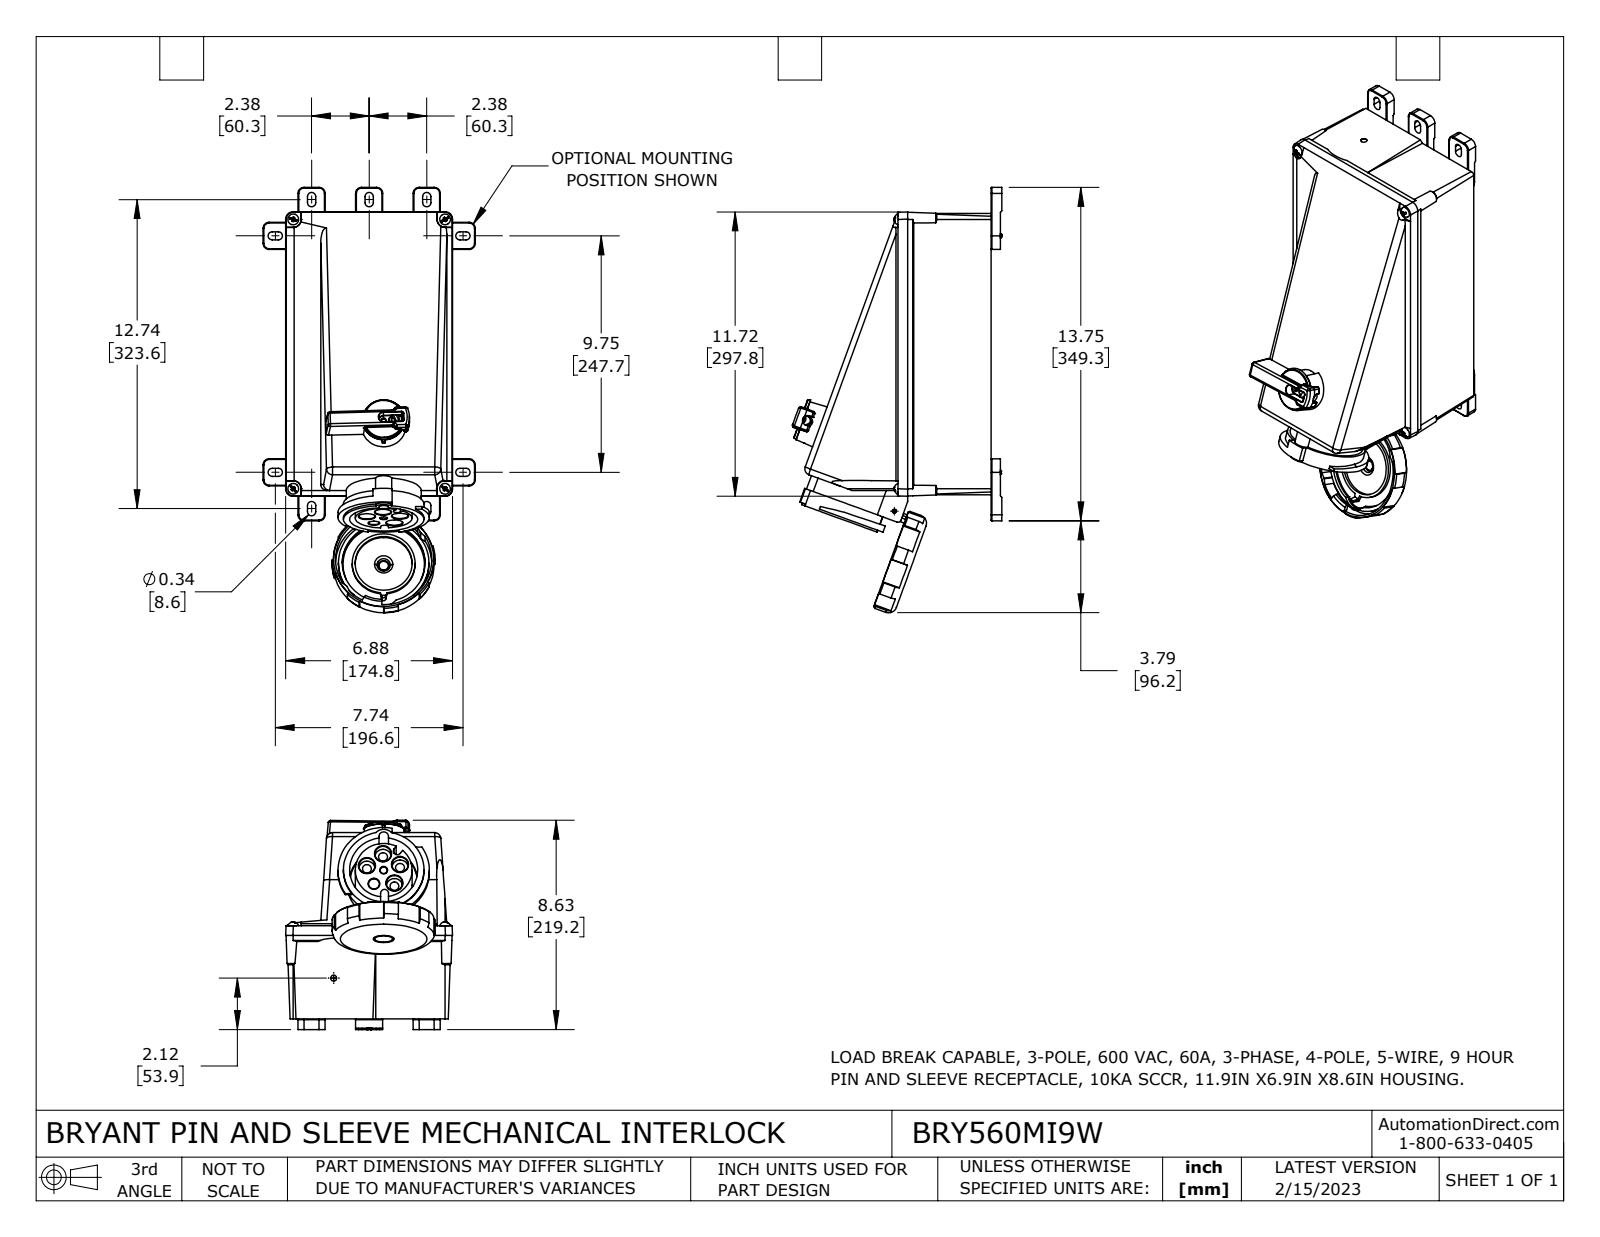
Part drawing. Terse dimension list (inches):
name: BRY560MI9W
written by: SolidWorks 2021 (CONFIG_CONTROL_DESIGN)
unit: in
bodies: 22 solids, 1825 faces (730 planar, 642 cylindrical, 453 other)
size: 17.544 × 8.635 × 6.88
volume: 423.1 in³; area: 846.5 in²
holes: 8× ⌀0.25, 5× ⌀0.253, 5× ⌀0.281, 4× ⌀0.078, 4× ⌀0.366, 4× ⌀0.666, 3× ⌀0.12, 2× ⌀0.094, 1× ⌀0.128, 1× ⌀0.159, 1× ⌀0.169, 1× ⌀0.19
bosses: 2× ⌀0.263, 1× ⌀3.73, 1× ⌀3.323, 1× ⌀3.091, 1× ⌀2.592, 1× ⌀2.342, 1× ⌀0.8, 1× ⌀0.72
rounds: 135× R0.015, 53× R0.03, 30× R0.08, 24× R0.09, 16× R0.25, 12× R0.075, 10× R0.17, 5× R0.29
face distances: 3.44, 0.14, 11.594, 5.374, 0.165, 5.514, 0.025, 0.15, 6.817, 5.349
hole spacings: 0.7, 0.844, 1.367, 2.375, 0.718, 1.016, 5.548, 10.456
